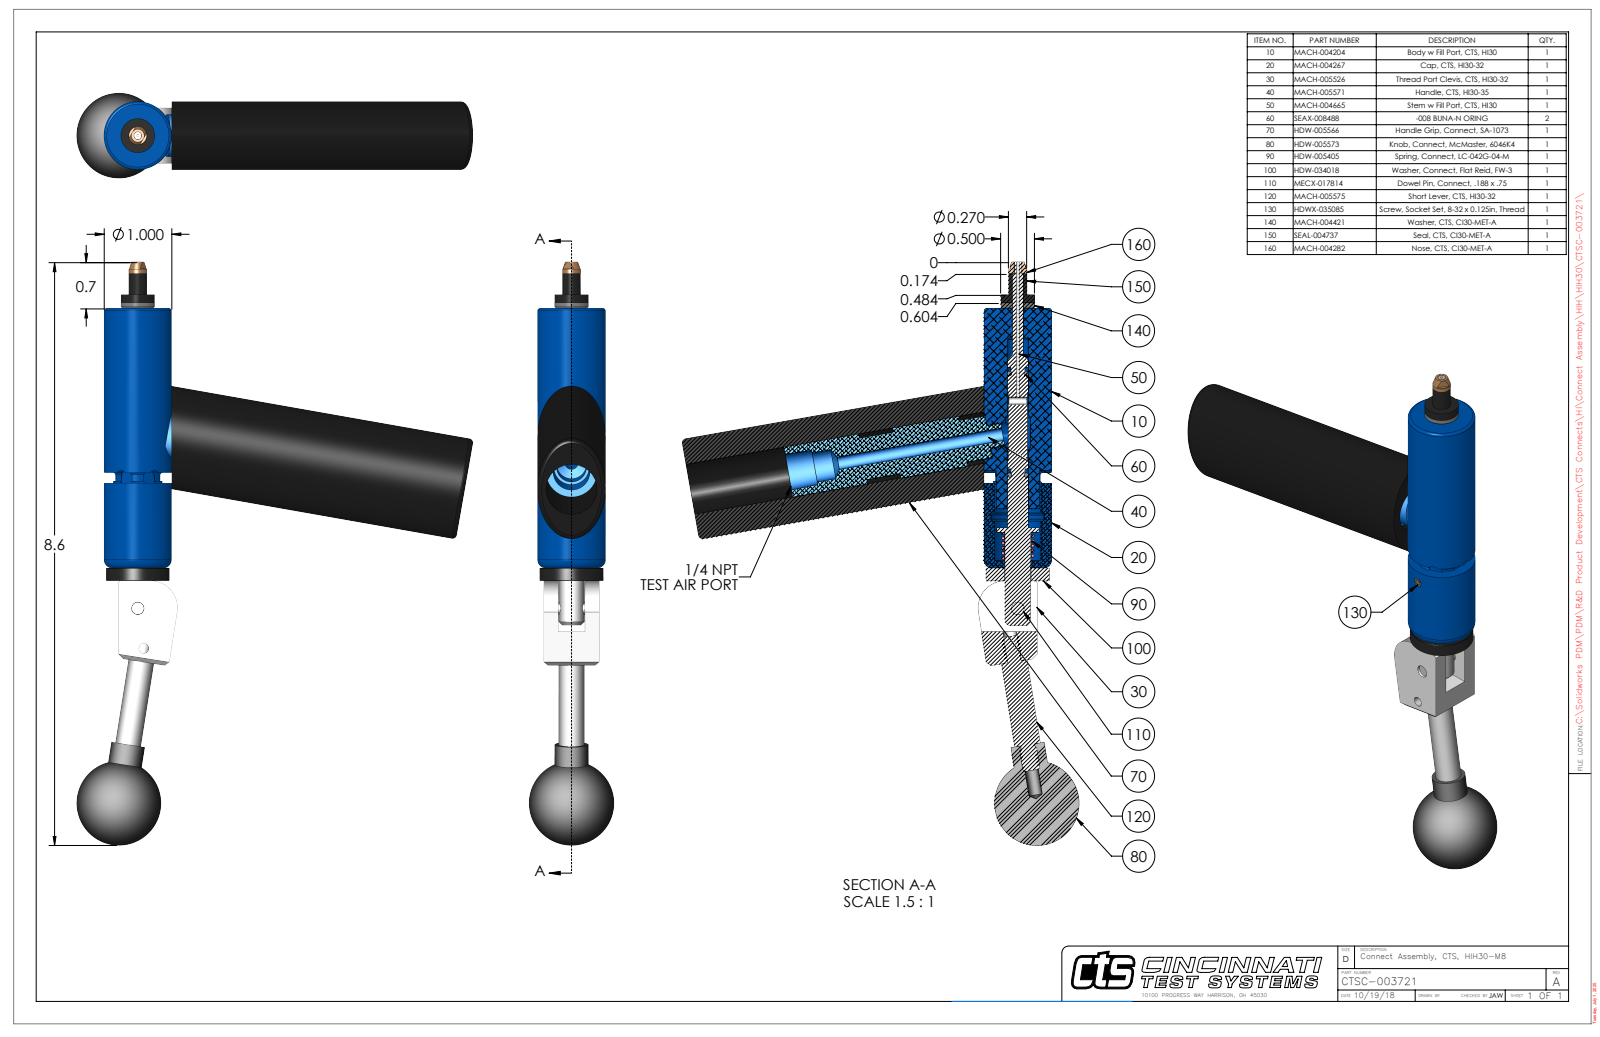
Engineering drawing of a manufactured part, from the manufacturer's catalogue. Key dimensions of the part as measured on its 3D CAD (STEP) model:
Part name (STEP PRODUCT): CTSC-003721
STEP written by: SolidWorks 2023 (AUTOMOTIVE_DESIGN)
Units: inches
Bodies: 10 solids, 306 faces (115 planar, 125 cylindrical, 66 other)
Overall size (bounding box): 8.618 × 5.856 × 1.25
Volume: 9.212 in³ · Surface area: 73.61 in²
Round holes (diameter × count): ⌀0.201 ×2, ⌀0.04 ×1, ⌀0.09 ×1, ⌀0.113 ×1, ⌀0.136 ×1, ⌀0.15 ×1, ⌀0.155 ×1, ⌀0.161 ×1, ⌀0.164 ×1, ⌀0.187 ×1, ⌀0.189 ×1, ⌀0.385 ×1
Round bosses / shafts (diameter × count): ⌀0.5 ×2, ⌀1 ×1, ⌀0.936 ×1, ⌀0.75 ×1, ⌀0.62 ×1, ⌀0.38 ×1, ⌀0.375 ×1, ⌀0.27 ×1
Partial cylindrical surfaces — rounded edges, fillets, slot ends (radius × count): R0.093 ×6, R0.015 ×1, R0.054 ×1, R0.325 ×1, R0.375 ×1, R0.4 ×1, R0.465 ×1, R0.476 ×1
Main face-to-face distances: 0.21, 0.602, 0.812, 3.837, 4.024, 0.187, 0.391, 0.785, 2.583, 1.253
Hole centre spacings: 0.599, 1.658, 2.252
